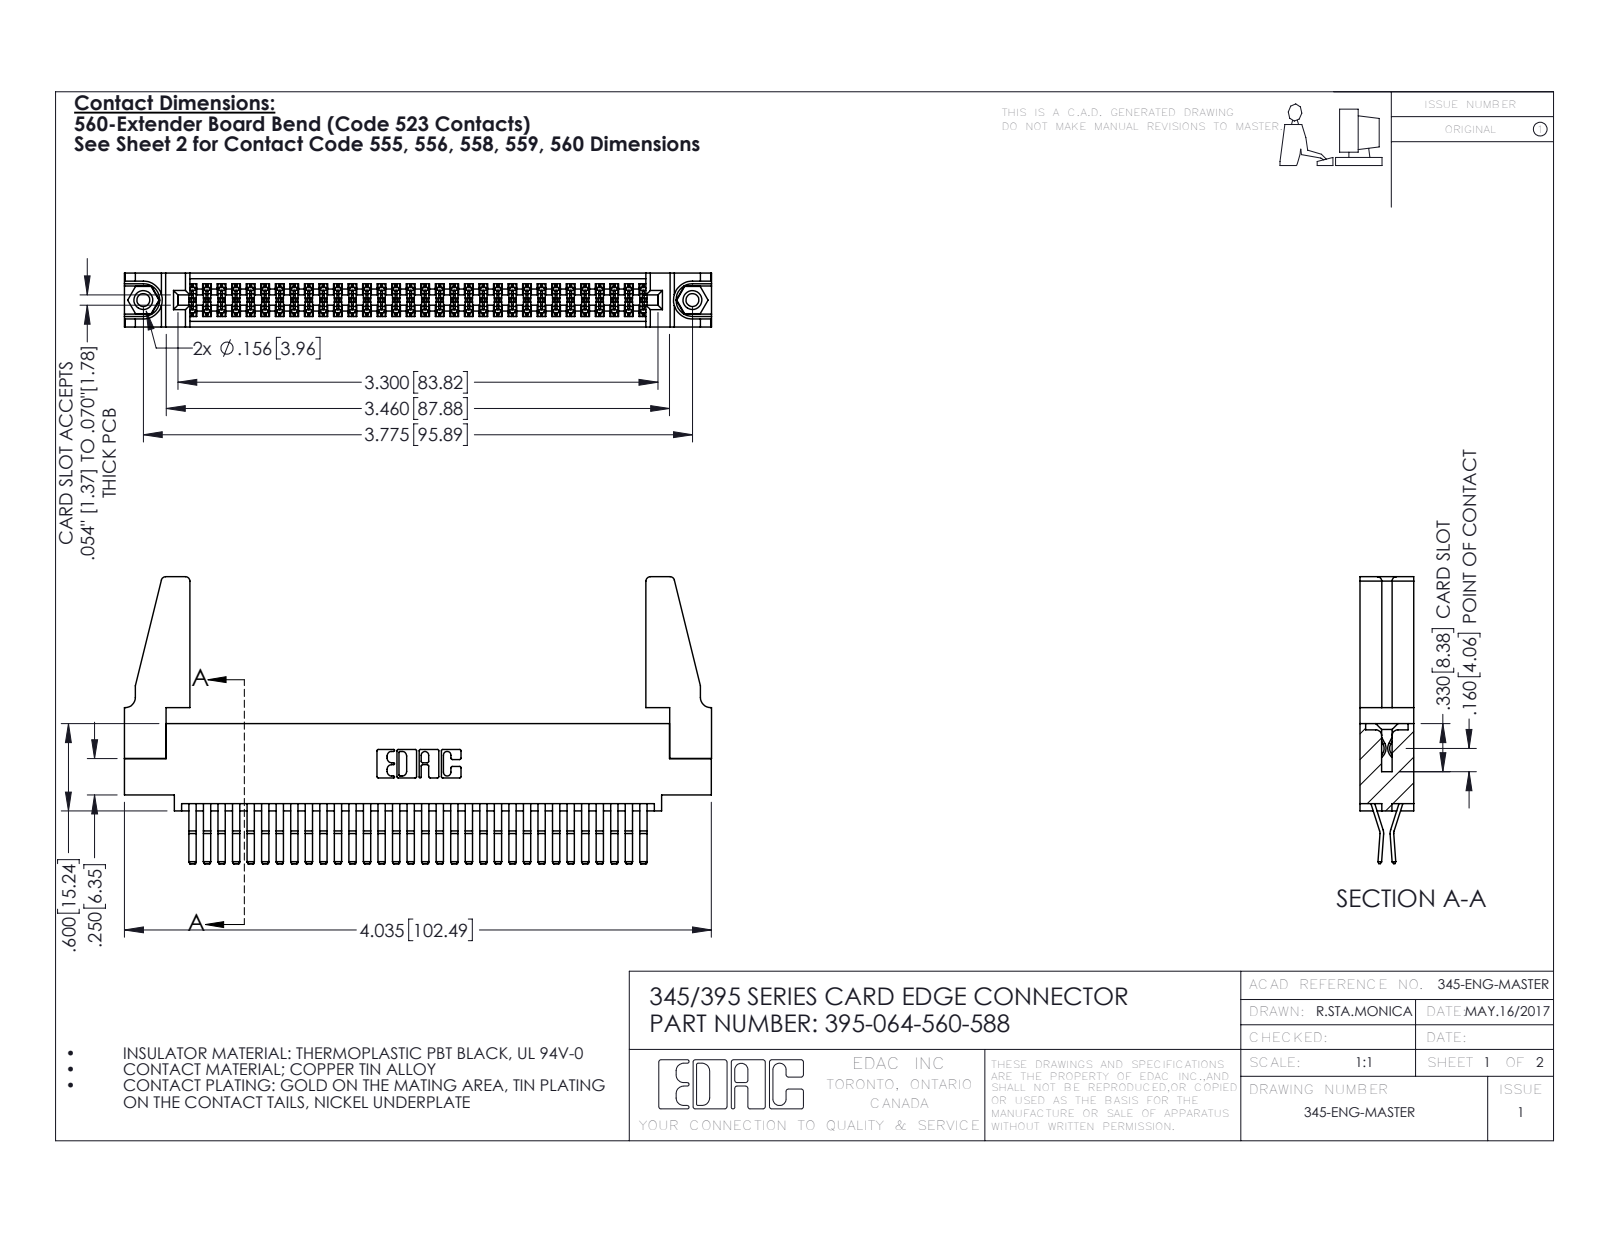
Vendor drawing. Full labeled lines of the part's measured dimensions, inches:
Part name (STEP PRODUCT): 345-292-001_560 Tail; 345 Part_0.110 Offset - 0.156 Dia-TH; 345-250-001_345-250-001-102; 345-220-078_345-220-088 (+1 more)
STEP written by: SolidWorks 2016 (CONFIG_CONTROL_DESIGN)
Units: inches
Bodies: 69 solids, 3582 faces (2268 planar, 1298 cylindrical, 16 other)
Overall size (bounding box): 4.036 × 1.972 × 0.37
Volume: 0.822 in³ · Surface area: 29.75 in²
Round holes (diameter × count): ⌀0.089 ×2, ⌀0.125 ×2, ⌀0.156 ×2, ⌀0.064 ×1
Round bosses / shafts (diameter × count): ⌀0.155 ×2
Partial cylindrical surfaces — rounded edges, fillets, slot ends (radius × count): R0.006 ×97, R0.01 ×22, R0.03 ×8, R0.007 ×6, R0.031 ×6, R0.026 ×3, R0.01 ×2, R0.014 ×2
Main face-to-face distances: 0.072, 0.298, 0.025, 0.37, 0.2, 0.098, 0.272, 0.225, 0.175, 0.149
Hole centre spacings: 0.27, 3.54, 3.775
